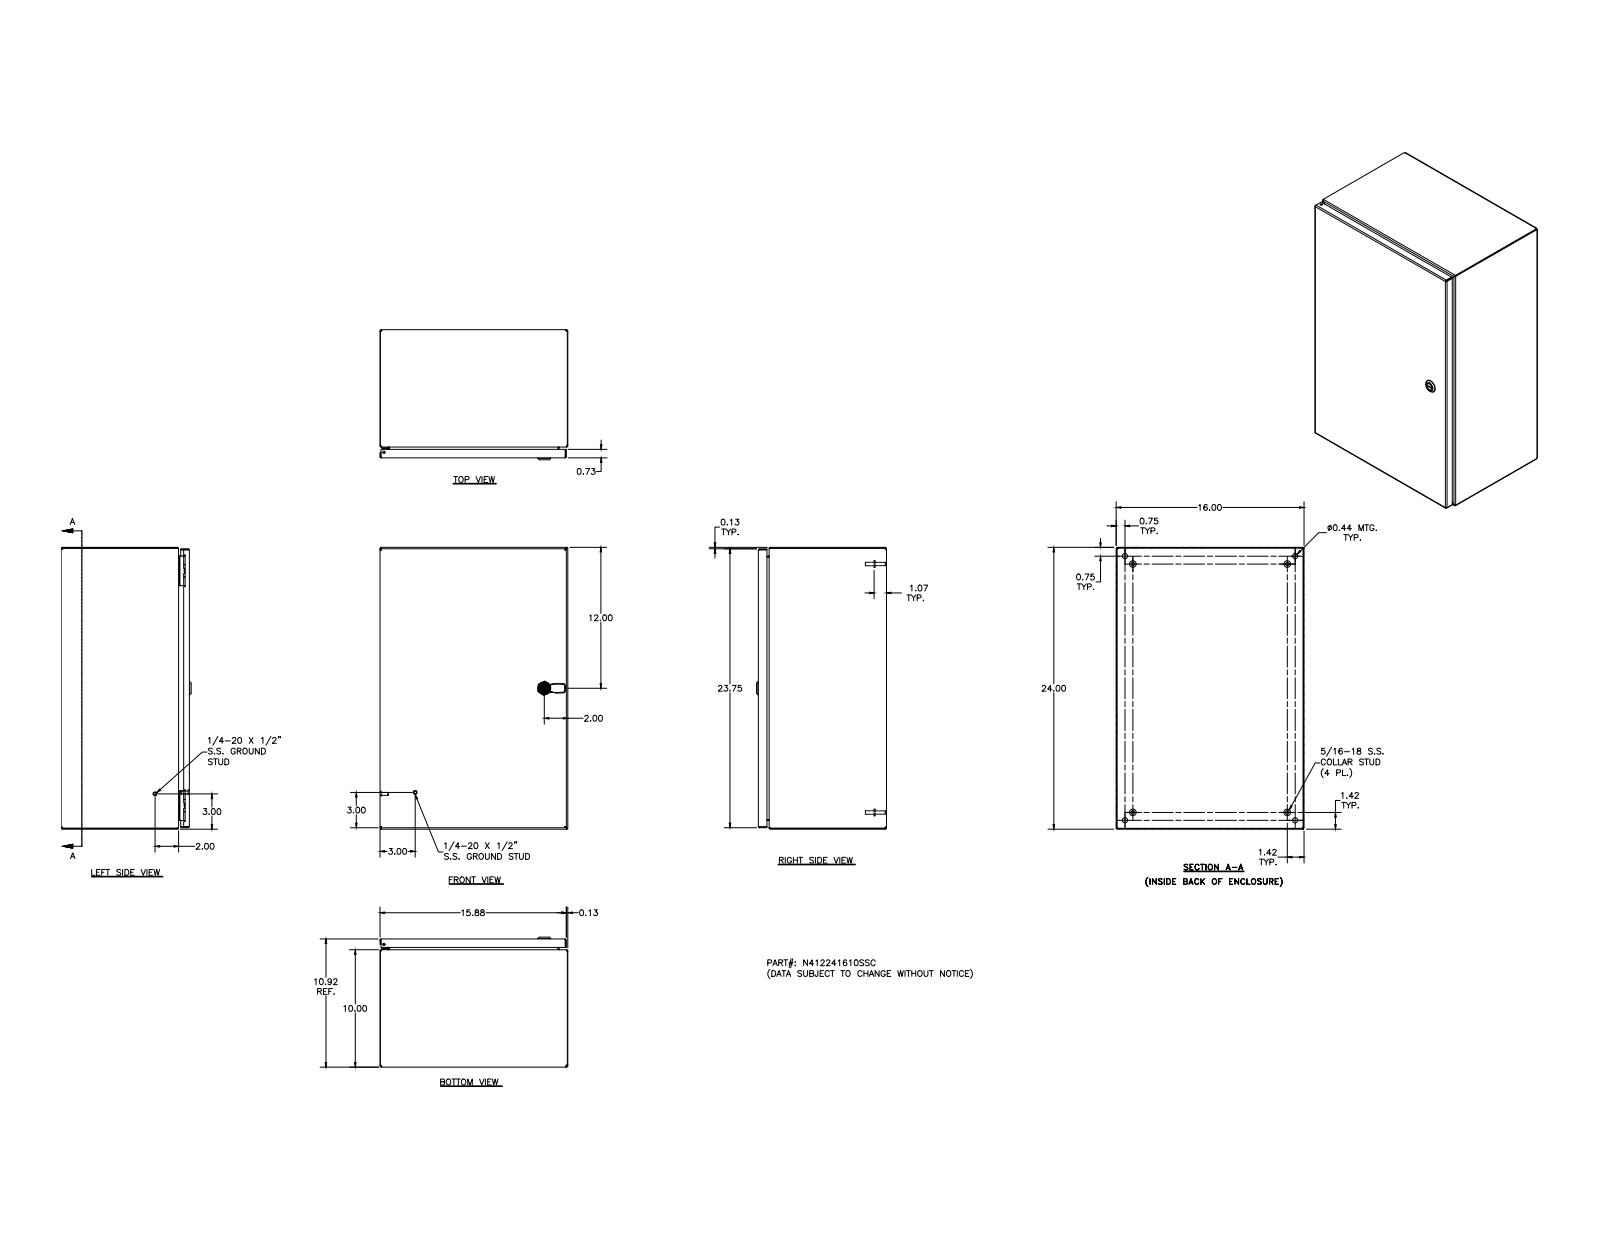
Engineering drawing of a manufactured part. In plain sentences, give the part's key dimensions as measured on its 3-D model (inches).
The part is named "N412241610SSC; N412241610SSCBKP; 388151; N4122416SSCLID (+8 more)". Its 3-D file was written by "Autodesk Inventor 2011 (AUTOMOTIVE_DESIGN)". It is 34 solids with 1384 faces: 531 planar, 509 cylindrical and 344 other. Overall it measures 24 by 16 by 11.075 inches. Its volume is 128 cubic inches and its surface area 3 480 square inches. Round holes: 5 of diameter 0.188, 4 of diameter 0.093, 4 of diameter 0.152, 4 of diameter 0.167, 4 of diameter 0.172, 4 of diameter 0.437, 2 of diameter 0.156, 1 of diameter 0.187, 1 of diameter 0.197, 1 of diameter 0.315, 1 of diameter 0.394, 1 of diameter 0.402. Round bosses or shafts: 10 of diameter 0.25, 4 of diameter 0.563, 4 of diameter 0.36, 4 of diameter 0.32, 4 of diameter 0.3, 4 of diameter 0.275, 4 of diameter 0.256, 4 of diameter 0.164. Partial cylindrical surfaces (rounded edges, fillets, slot ends): 30 of radius 0.031, 26 of radius 0.05, 20 of radius 0.105, 18 of radius 0.016, 14 of radius 0.125, 9 of radius 0.02, 8 of radius 0.032, 8 of radius 0.07. The main face-to-face distances are 0.074, 10.843, 15.926, 10.769, 10.917, 23.926, 15.852, 16, 24, 23.852. The hole center spacings are 20, 0.017, 0.66, 0.019, 0.5, 0.648, 0.652, 0.656.
